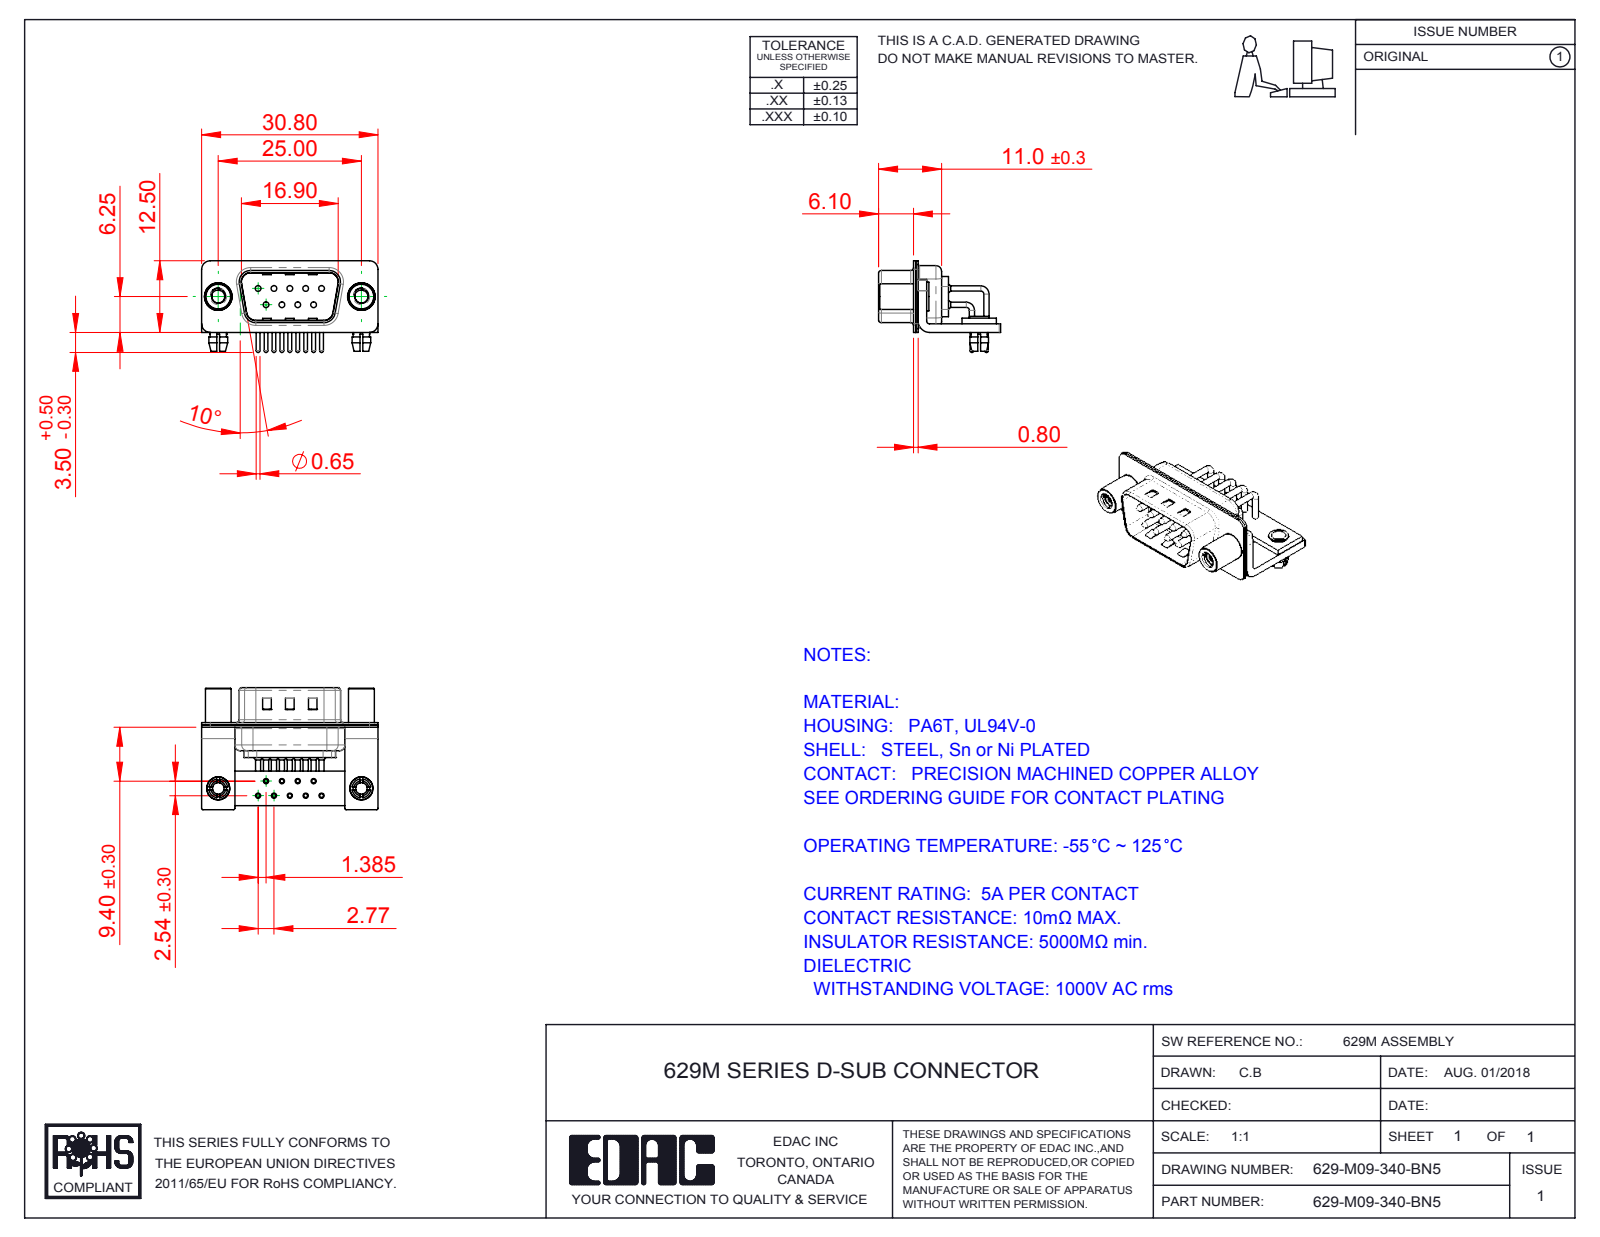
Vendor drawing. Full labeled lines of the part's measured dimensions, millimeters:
Part name (STEP PRODUCT): 629M 4-40 Threaded Standoff; 629M Stabilizer Bracket; 629M Shell Front_09 Contacts; 629M Contact Row 2 (+6 more)
STEP written by: SolidWorks 2016 (CONFIG_CONTROL_DESIGN)
Units: millimetres
Bodies: 19 solids, 1504 faces (759 planar, 567 cylindrical, 178 other)
Overall size (bounding box): 30.8 × 21.3 × 16
Volume: 1 984 mm³ · Surface area: 5 510 mm²
Round holes (diameter × count): ⌀2 ×11, ⌀0.9 ×9, ⌀1 ×9, ⌀1.7 ×9, ⌀2.26 ×2, ⌀2.5 ×2, ⌀3.2 ×2, ⌀4 ×2, ⌀4.8 ×2
Round bosses / shafts (diameter × count): ⌀1.5 ×9, ⌀0.9 ×9, ⌀0.65 ×9, ⌀5 ×2, ⌀4.9 ×2, ⌀4.5 ×2, ⌀4 ×2, ⌀3.4 ×2
Partial cylindrical surfaces — rounded edges, fillets, slot ends (radius × count): R0.25 ×16, R1.5 ×16, R2 ×13, R0.5 ×9, R1.01 ×9, R1.6 ×8, R0.6 ×4, R0.65 ×4
Main face-to-face distances: 0.4, 1.5, 0.8, 0.85, 1.25, 1.9, 1, 2.5, 10.4, 9.55
Hole centre spacings: 2.77, 5.54, 3.16, 4.87, 8.31, 2.89, 2.9, 5.03
